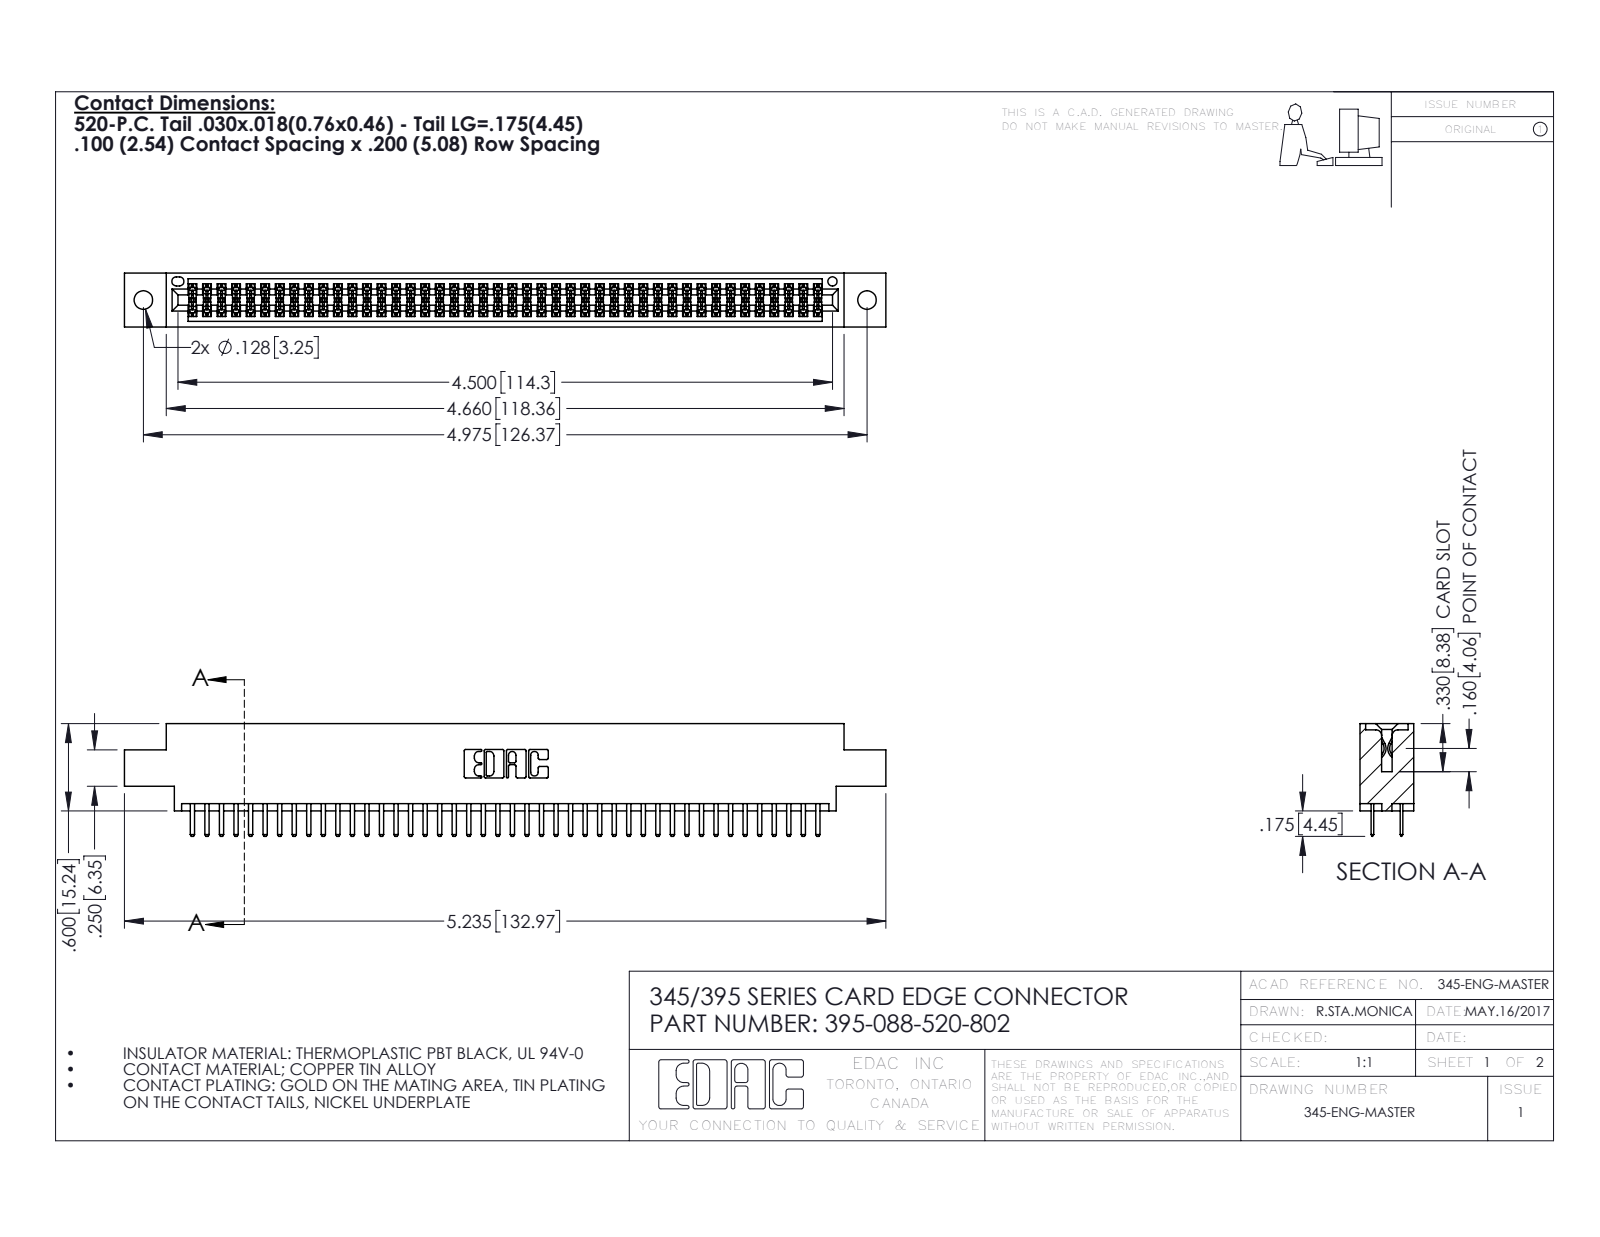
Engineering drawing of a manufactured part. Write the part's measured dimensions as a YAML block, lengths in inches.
part_name: "395-088-520-802; 345-292-001_345-293-120; 345 Part_0.170 Offset - 0.128 Dia"
step_written_by: "SolidWorks 2016 (CONFIG_CONTROL_DESIGN)"
units: inches
bodies: {solids: 89, faces: 4882, planar: 3164, cylindrical: 1718, other: 0}
overall_size: [5.235, 0.775, 0.37]
volume: 0.778
surface_area: 28.94
round_holes:
  - {diameter: 0.128, count: 2}
  - {diameter: 0.064, count: 1}
partial_cylinders:
  - {radius: 0.006, count: 132}
  - {radius: 0.01, count: 92}
  - {radius: 0.01, count: 22}
  - {radius: 0.007, count: 6}
  - {radius: 0.031, count: 6}
  - {radius: 0.026, count: 3}
  - {radius: 0.014, count: 2}
  - {radius: 0.019, count: 2}
face_to_face_distances: [0.298, 0.072, 0.2, 0.37, 0.098, 0.272, 0.025, 0.225, 0.022, 0.175]
hole_center_spacings: [0.27, 4.739, 4.975]
